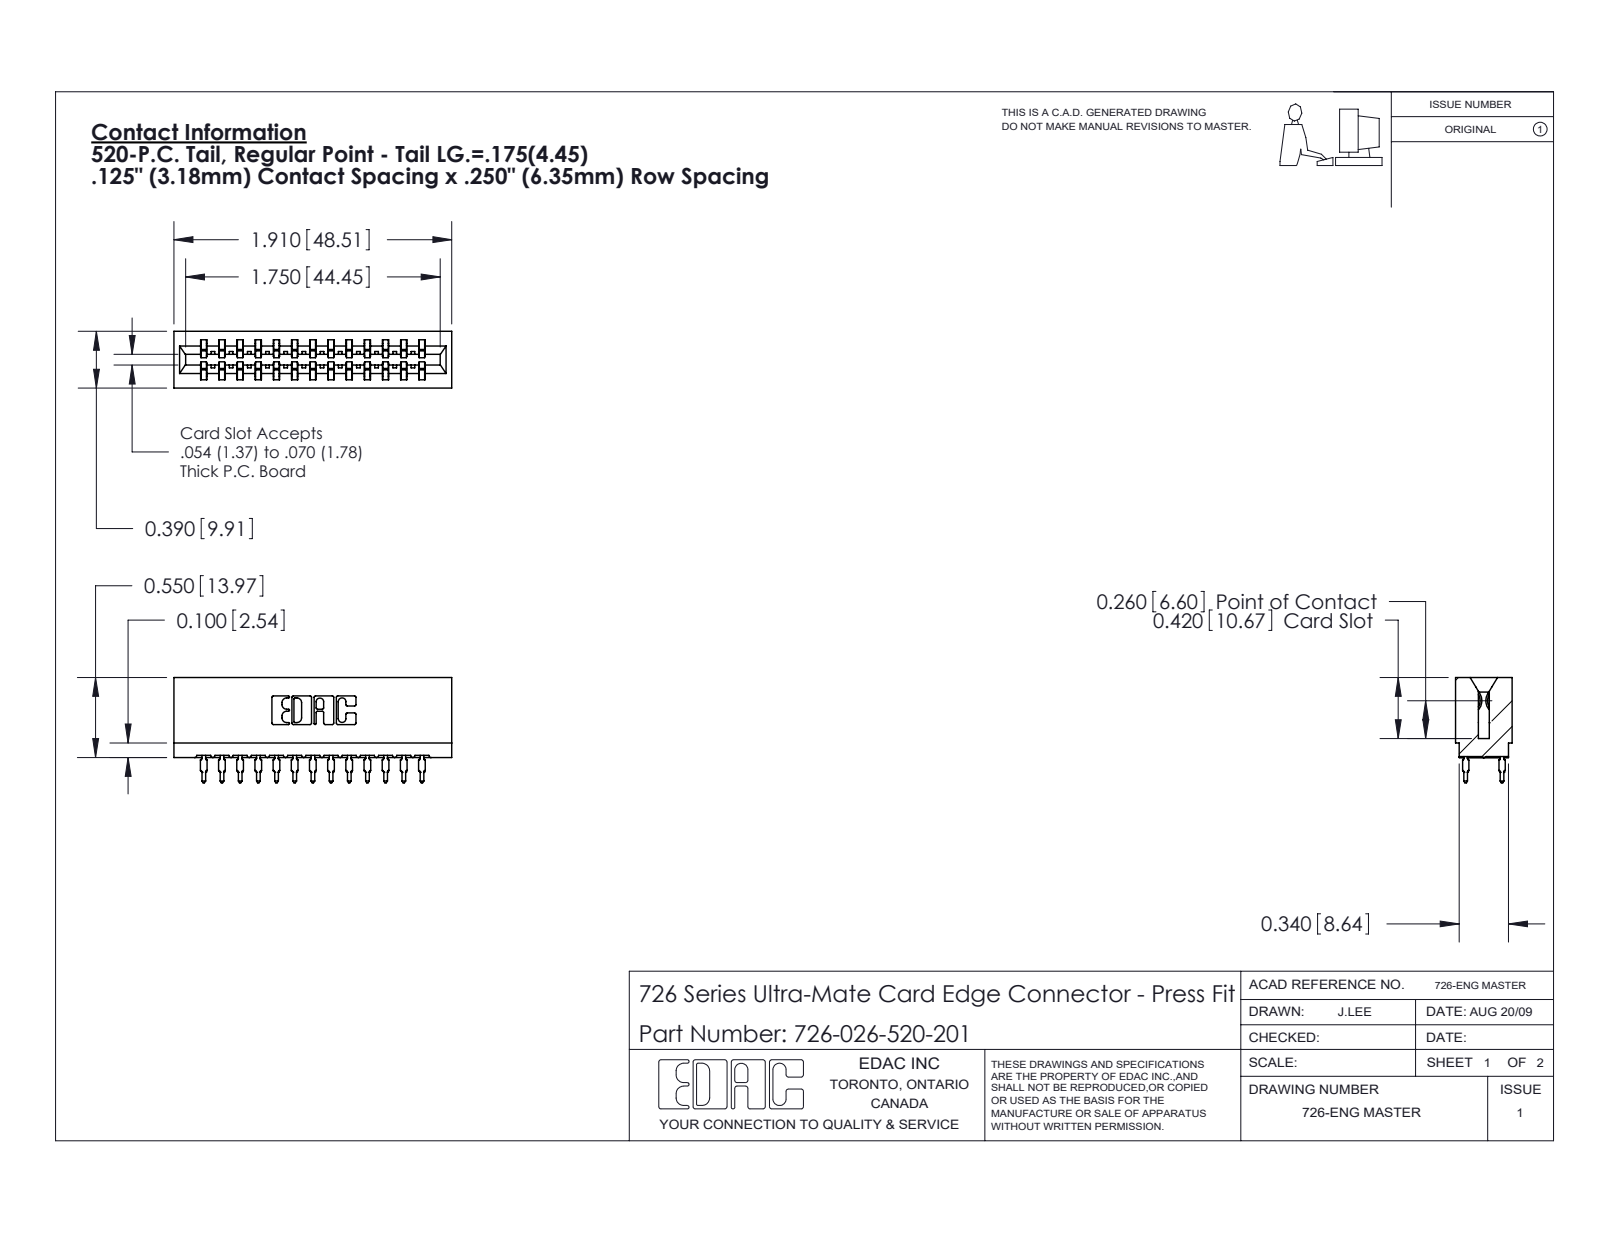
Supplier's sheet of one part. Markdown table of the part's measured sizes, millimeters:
| quantity | value |
| --- | --- |
| part name | 726-026-520-201; 726 Part_.515 Slot Depth - 01; 746-292-001_520 |
| STEP written by | SolidWorks 2020 (CONFIG_CONTROL_DESIGN) |
| units | millimeters |
| bodies | 27 solids, 2424 faces (1251 planar, 497 cylindrical, 676 other) |
| overall size | 48.5 × 18.4 × 9.9 |
| volume | 4 590 mm³ |
| surface area | 7 032 mm² |
| partial cylindrical surfaces (radius × count) | 0.5 × 52, 0.3 × 22, 0.4 × 14, 0.1 × 8, 0.3 × 8, 0.2 × 6, 0.8 × 6, 0.7 × 3 |
| main face-to-face distances | 6.4, 1.4, 8.5, 12.7, 19.1, 9.9, 0.6, 3.2, 13.8, 3.2 |
